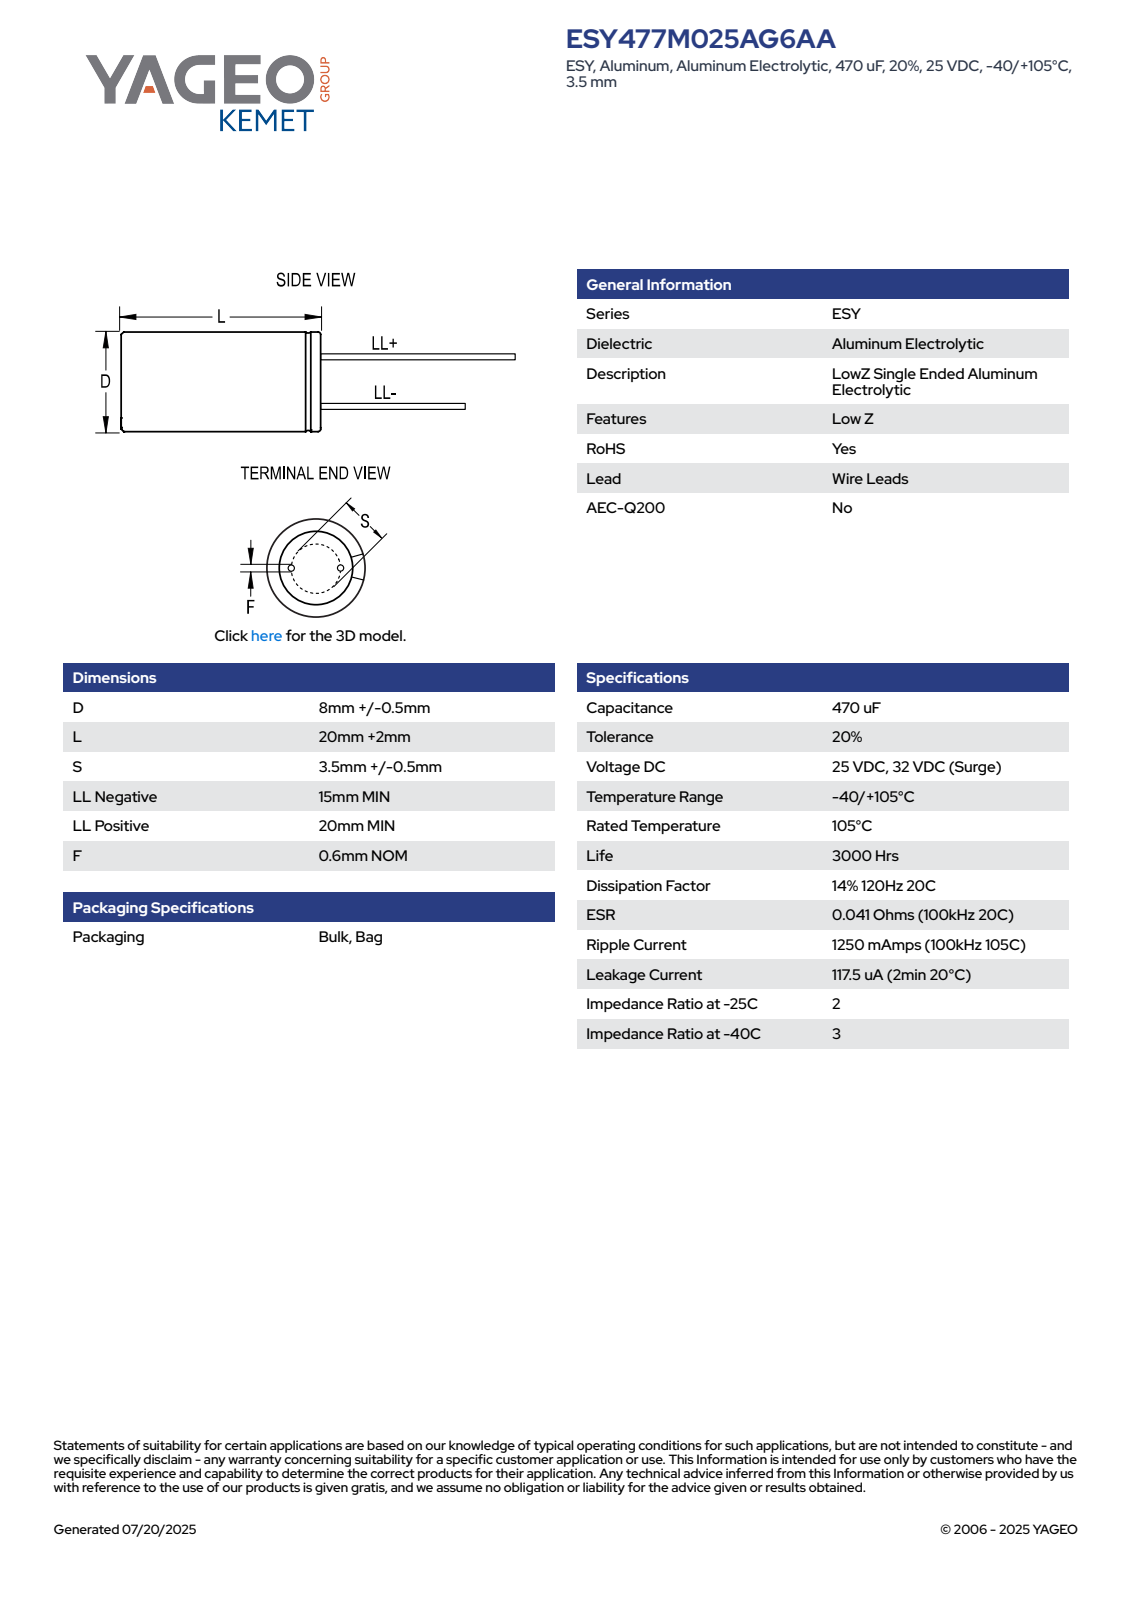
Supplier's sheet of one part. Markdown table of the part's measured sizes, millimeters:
| quantity | value |
| --- | --- |
| part name | CAR_KLP_8X20_D8.5L22S3.5F0.6 |
| STEP written by | SolidWorks 2014 (AUTOMOTIVE_DESIGN) |
| units | millimeters |
| bodies | 4 solids, 75 faces (61 planar, 8 cylindrical, 6 other) |
| overall size | 42.01 × 8.5 × 8.5 |
| volume | 1 252 mm³ |
| surface area | 783 mm² |
| round bosses / shafts (diameter × count) | 0.6 × 2, 8.5 × 1 |
| main face-to-face distances | 22, 22.01, 37.01, 42.01, 37, 42, 15, 20, 5, 1.15 |
